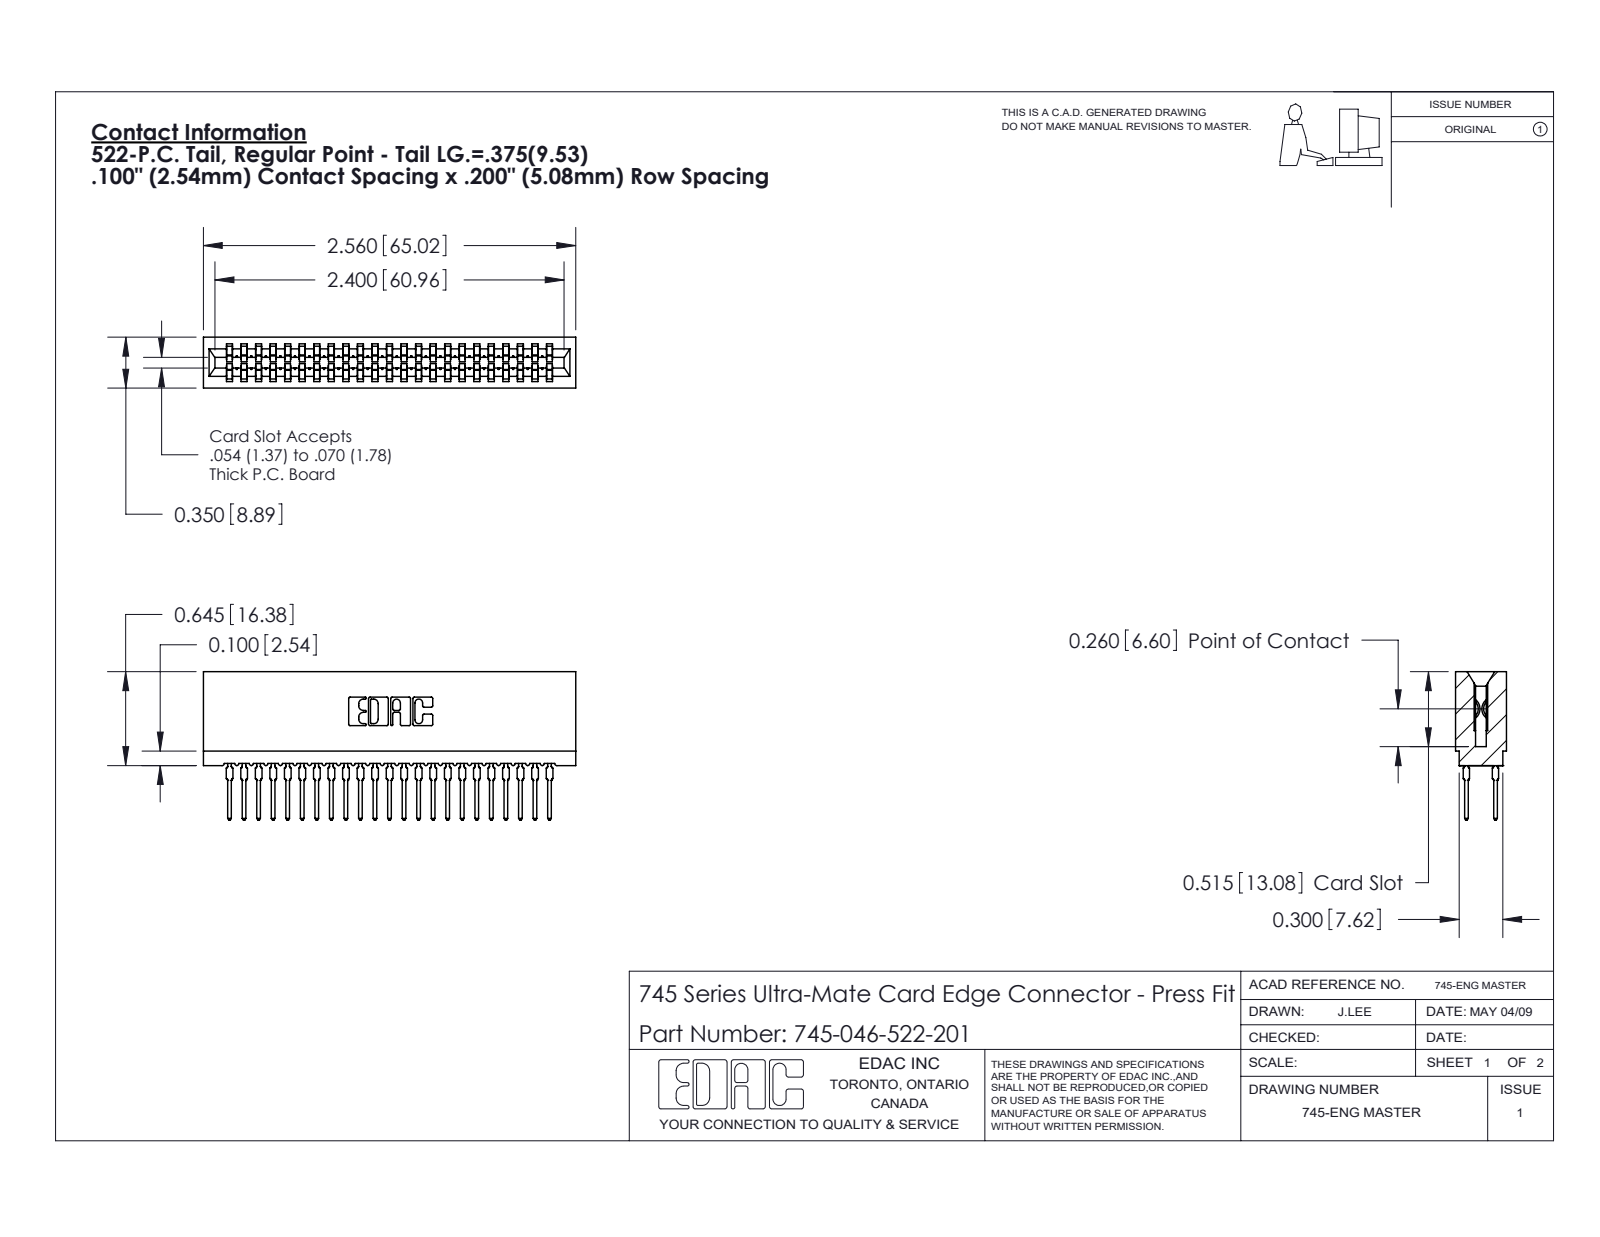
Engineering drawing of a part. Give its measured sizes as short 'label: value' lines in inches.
name: 745 Part_Insulator Option - 01; 745-046-522-201; 745-292-001_522
written by: SolidWorks 2020 (CONFIG_CONTROL_DESIGN)
unit: in
bodies: 47 solids, 4212 faces (2171 planar, 845 cylindrical, 1196 other)
size: 2.56 × 1.021 × 0.35
volume: 0.367 in³; area: 18.53 in²
rounds: 92× R0.021, 46× R0.015, 22× R0.01, 8× R0.005, 8× R0.011, 6× R0.007, 6× R0.031, 3× R0.026
face distances: 0.2, 0.1, 0.35, 0.063, 0.287, 0.3, 0.138, 0.212, 0.076, 0.149
